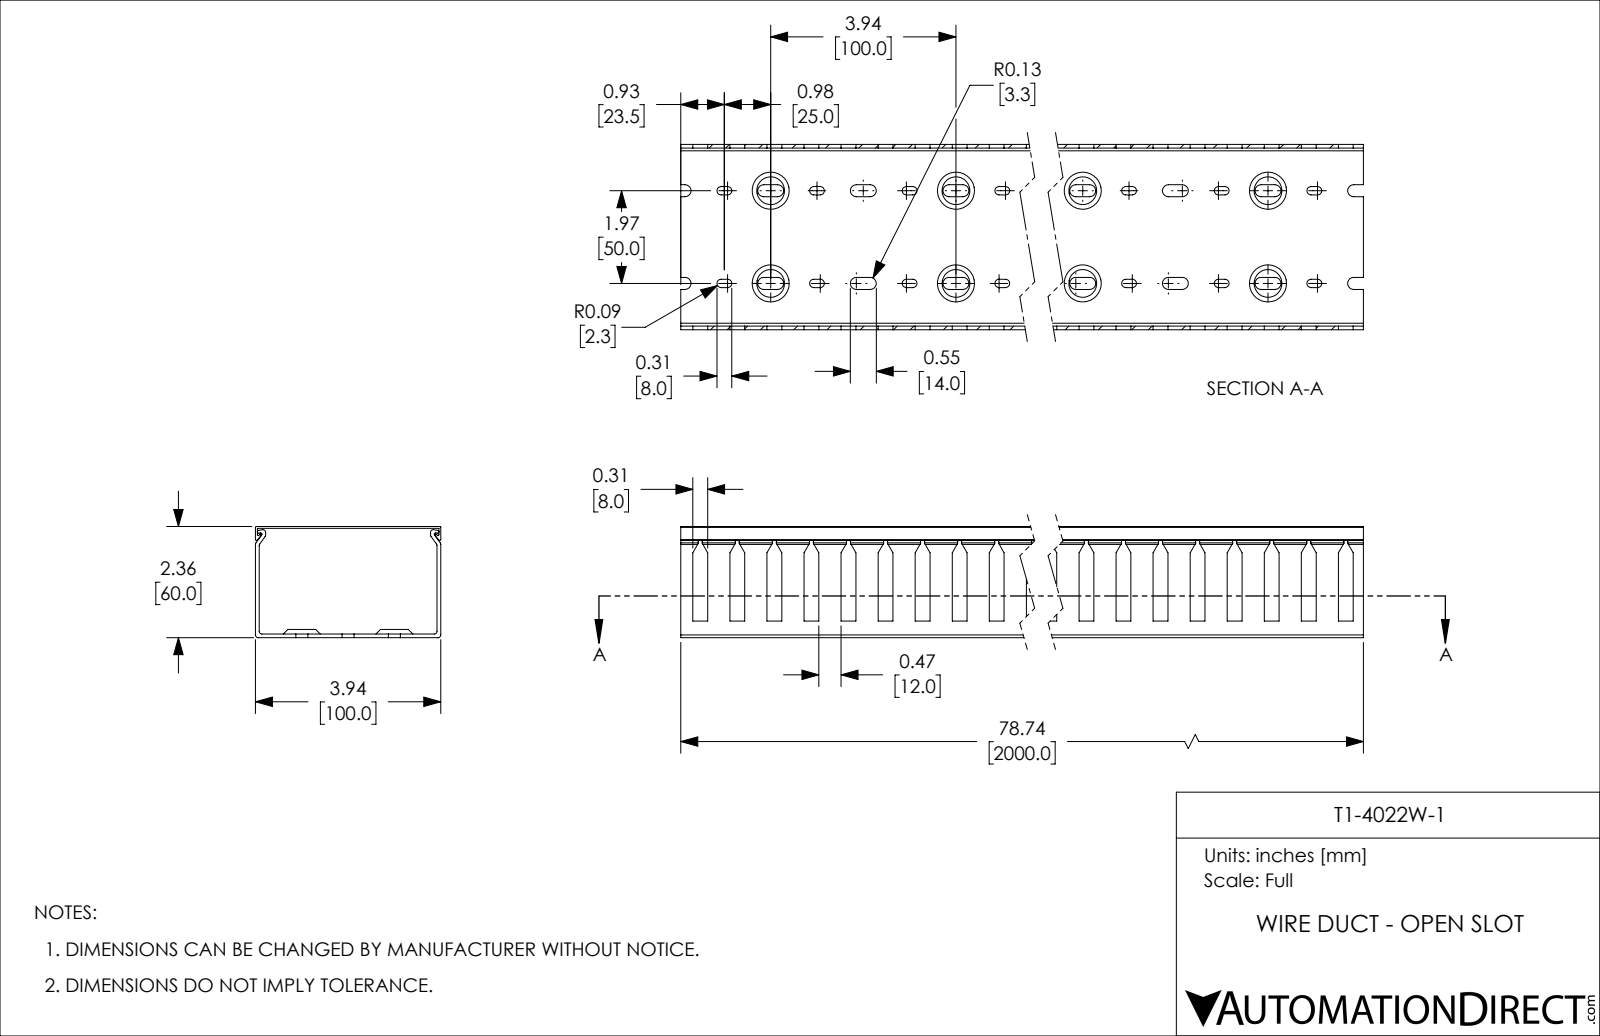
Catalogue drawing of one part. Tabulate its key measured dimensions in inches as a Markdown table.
| quantity | value |
| --- | --- |
| part name | T1-4022W-1 |
| STEP written by | SolidWorks 2021 (CONFIG_CONTROL_DESIGN) |
| units | inches |
| bodies | 2 solids, 1573 faces (762 planar, 731 cylindrical, 80 other) |
| overall size | 78.74 × 3.937 × 2.362 |
| volume | 66.52 in³ |
| surface area | 2 058 in² |
| partial cylindrical surfaces (radius × count) | 0.128 × 200, 0.089 × 160, 0.059 × 12, 0.02 × 8, 0.03 × 6 |
| main face-to-face distances | 0.079, 0.039, 2.362, 3.858, 2.323, 2.244, 2.283, 3.937, 3.78, 3.898 |
